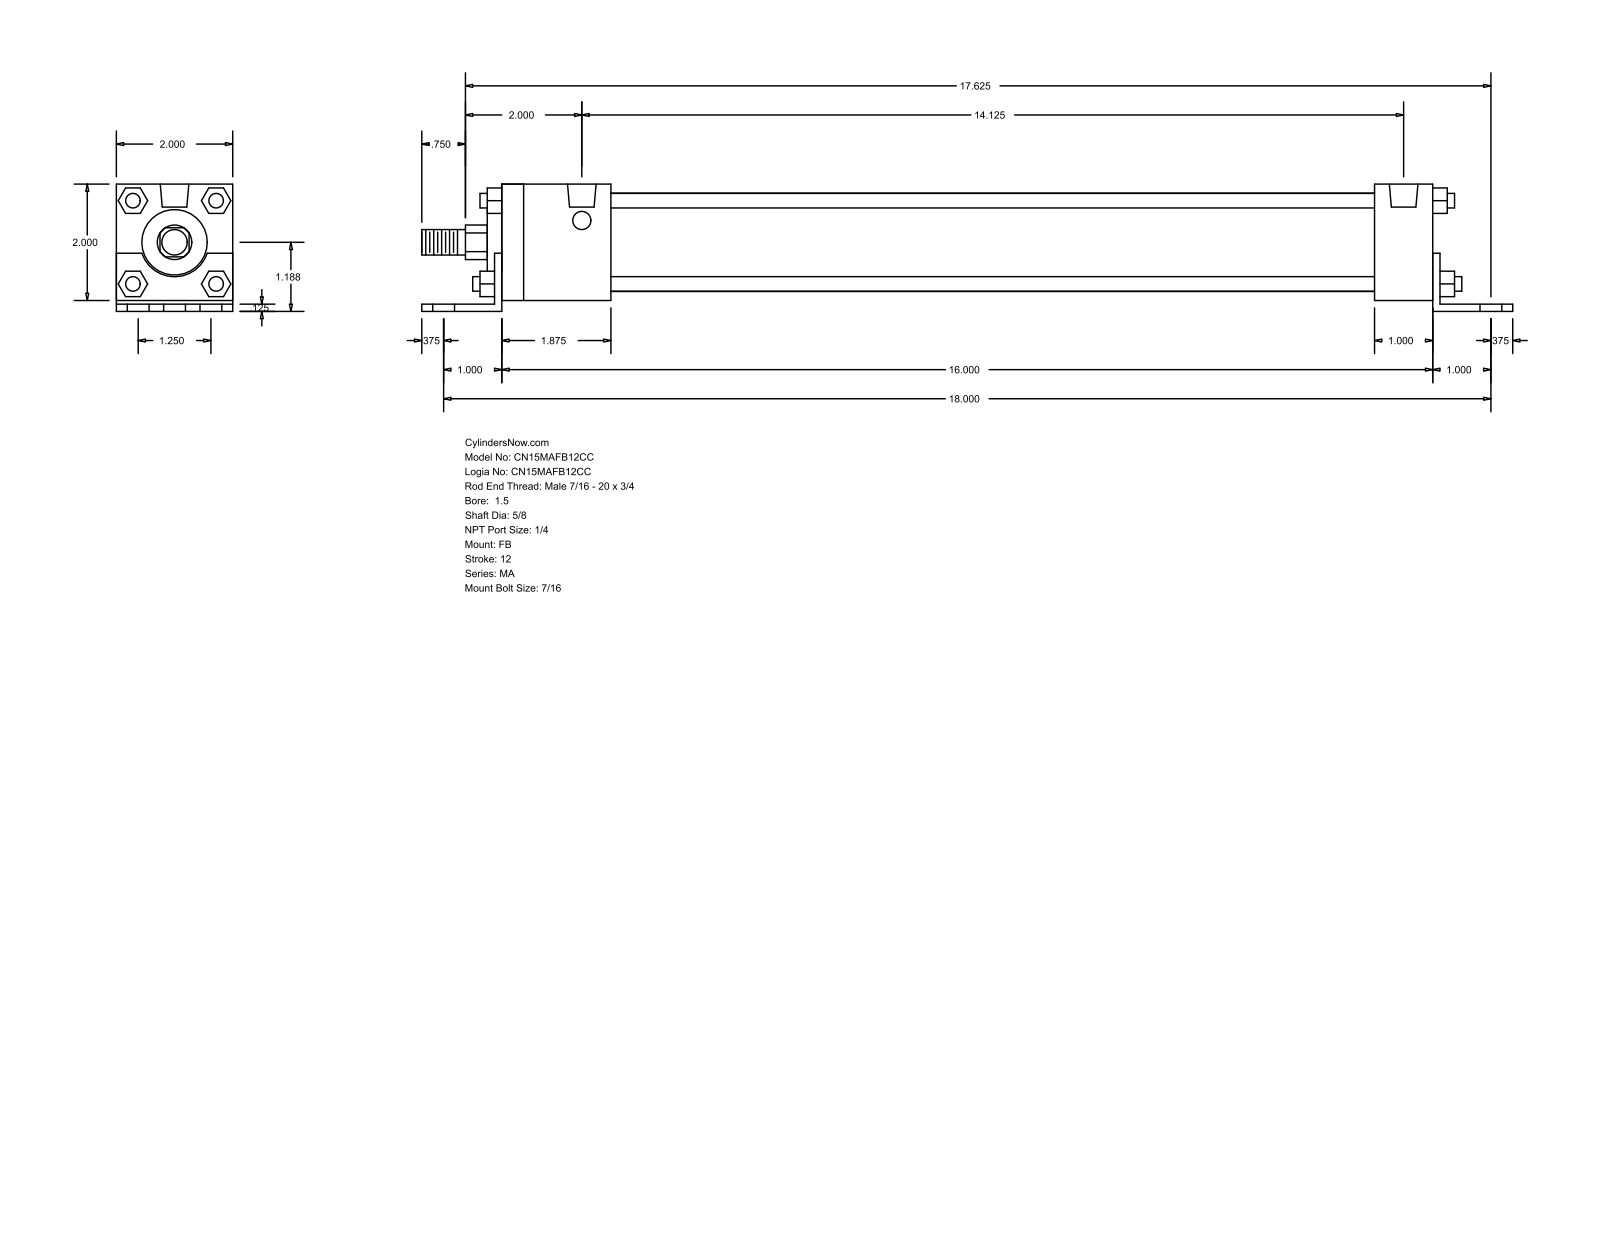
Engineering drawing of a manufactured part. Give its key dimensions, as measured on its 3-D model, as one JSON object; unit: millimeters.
{"part_name": "MA_FB__0150_0.625", "step_written_by": "GSSL Pune (CONFIG_CONTROL_DESIGN)", "units": "millimeters", "bodies": {"solids": 0, "faces": 140, "planar": 105, "cylindrical": 35, "other": 0}, "overall_size": [476.25, 55.56, 50.8], "round_holes": [[11.11, 6], [7.94, 4], [12.49, 2]], "round_bosses_or_shafts": [[6.35, 4], [42.93, 1], [28.57, 1], [15.88, 1], [11.11, 1]], "partial_cylinders_radius": [[7.54, 1], [15.05, 1]], "face_to_face_distances": [50.8, 3.17, 4.76, 55.56, 1.59, 52.39, 3.18, 409.57, 6.35, 415.92], "hole_center_spacings": [15.88, 457.49, 457.21, 31.76, 41.29, 62.38, 358.77, 397.2]}
